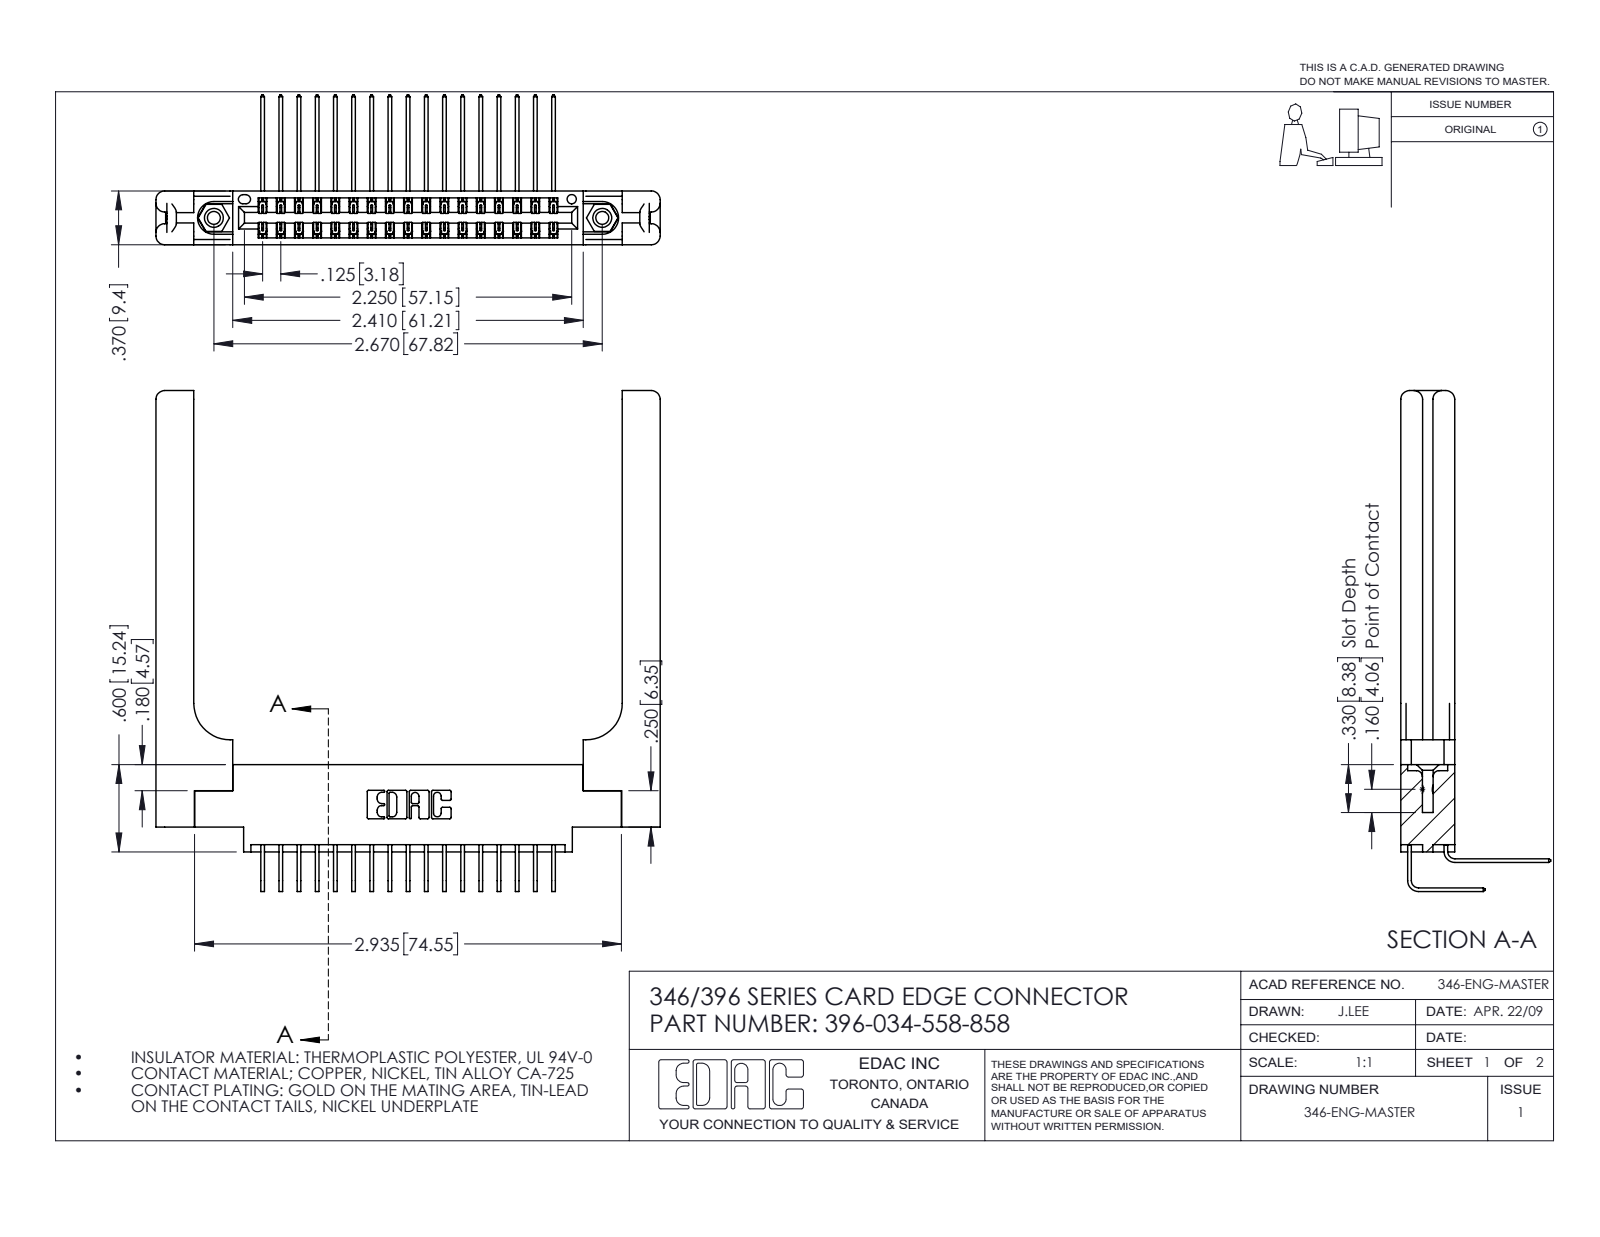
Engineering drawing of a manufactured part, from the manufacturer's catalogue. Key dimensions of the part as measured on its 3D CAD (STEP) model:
Part name (STEP PRODUCT): 396-034-558-858; 346 Part_0.170 Offset - 0.156 Dia-TH; 345-292-001_558 Tail - 2; 345-250-001_345-250-001-102 (+2 more)
STEP written by: SolidWorks 2016 (CONFIG_CONTROL_DESIGN)
Units: inches
Bodies: 39 solids, 2218 faces (1486 planar, 672 cylindrical, 60 other)
Overall size (bounding box): 3.466 × 3.443 × 1.03
Volume: 0.972 in³ · Surface area: 26.8 in²
Round holes (diameter × count): ⌀0.089 ×2, ⌀0.125 ×2, ⌀0.156 ×2, ⌀0.064 ×1
Round bosses / shafts (diameter × count): ⌀0.155 ×2
Partial cylindrical surfaces — rounded edges, fillets, slot ends (radius × count): R0.006 ×51, R0.01 ×22, R0.06 ×16, R0.007 ×6, R0.031 ×6, R0.026 ×3, R0.014 ×2, R0.022 ×2
Main face-to-face distances: 0.37, 0.072, 0.322, 0.048, 0.15, 0.148, 0.025, 0.25, 0.298, 0.077
Hole centre spacings: 0.246, 2.463, 2.67
